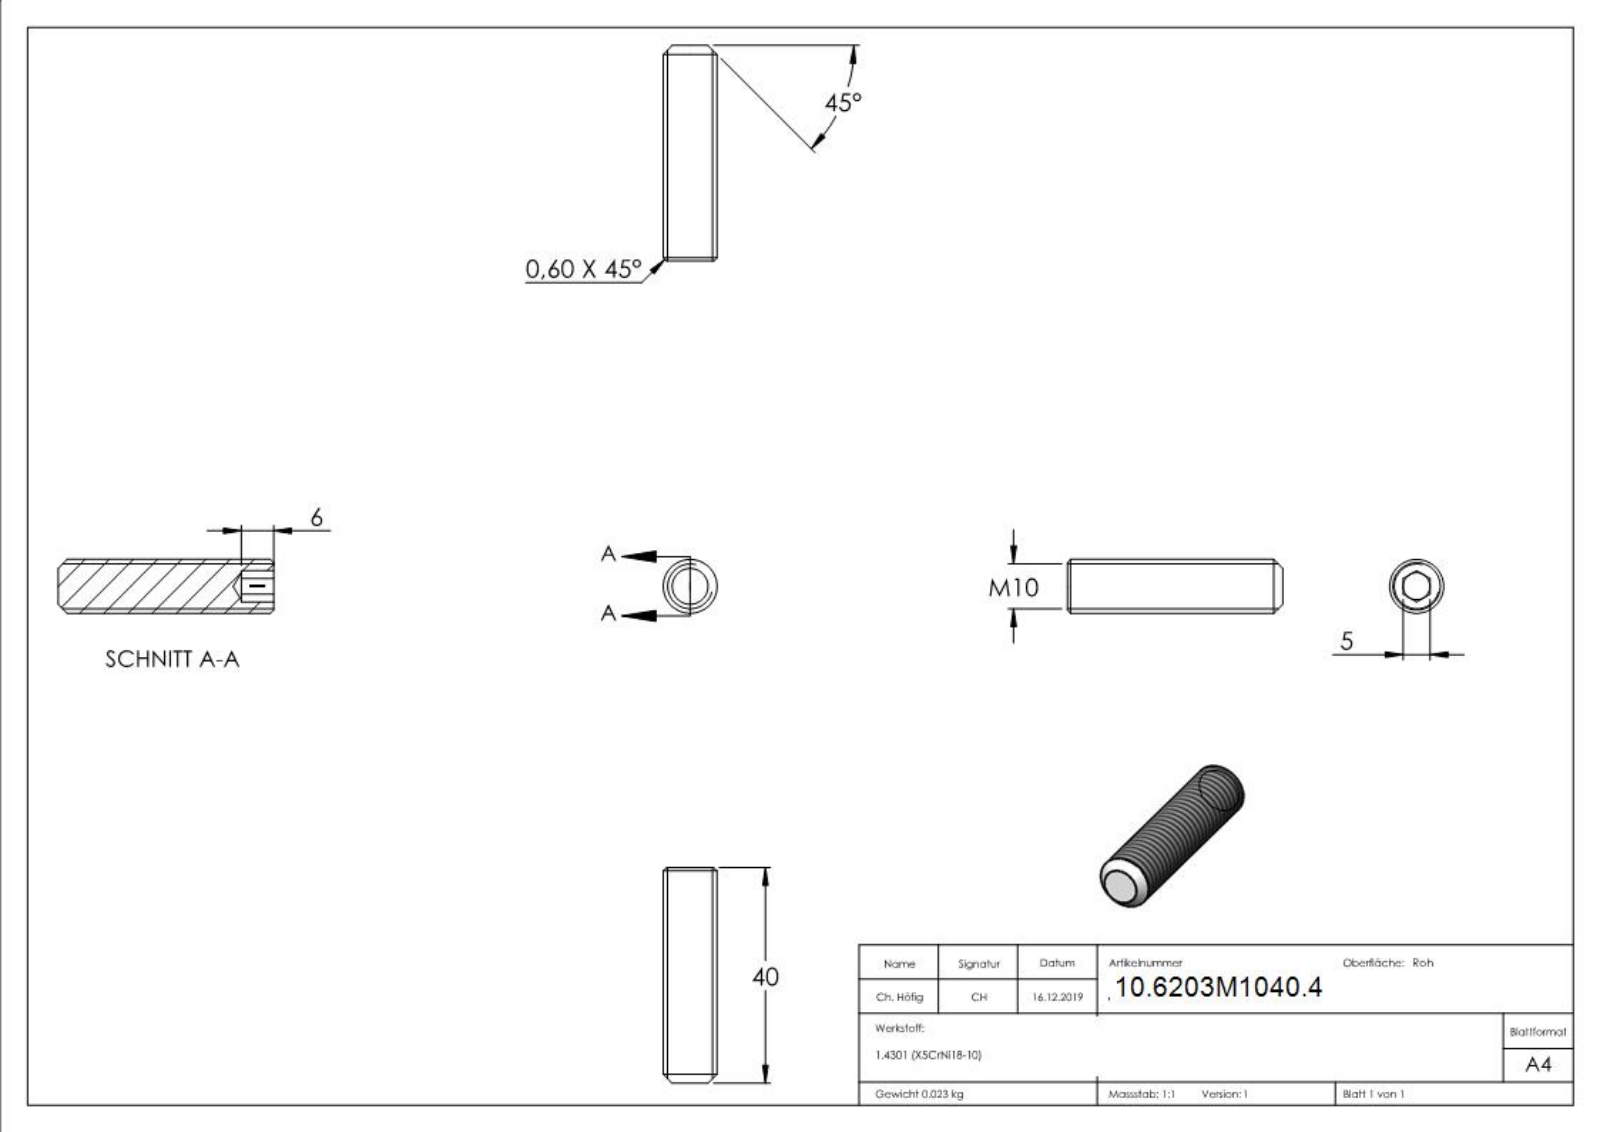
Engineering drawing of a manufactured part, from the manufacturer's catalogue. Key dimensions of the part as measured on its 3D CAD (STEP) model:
Part name (STEP PRODUCT): 58301-240-40
STEP written by: SolidWorks 2015 (CONFIG_CONTROL_DESIGN)
Units: millimetres
Bodies: 1 solid, 291 faces (152 planar, 1 cylindrical, 138 other)
Overall size (bounding box): 110 × 10 × 10
Volume: 2 957 mm³ · Surface area: 1 476 mm²
Round bosses / shafts (diameter × count): ⌀10 ×1
Main face-to-face distances: 5, 40, 34, 6, 5.1, 0.37, 0.96, 0.82, 0.31, 2.51
